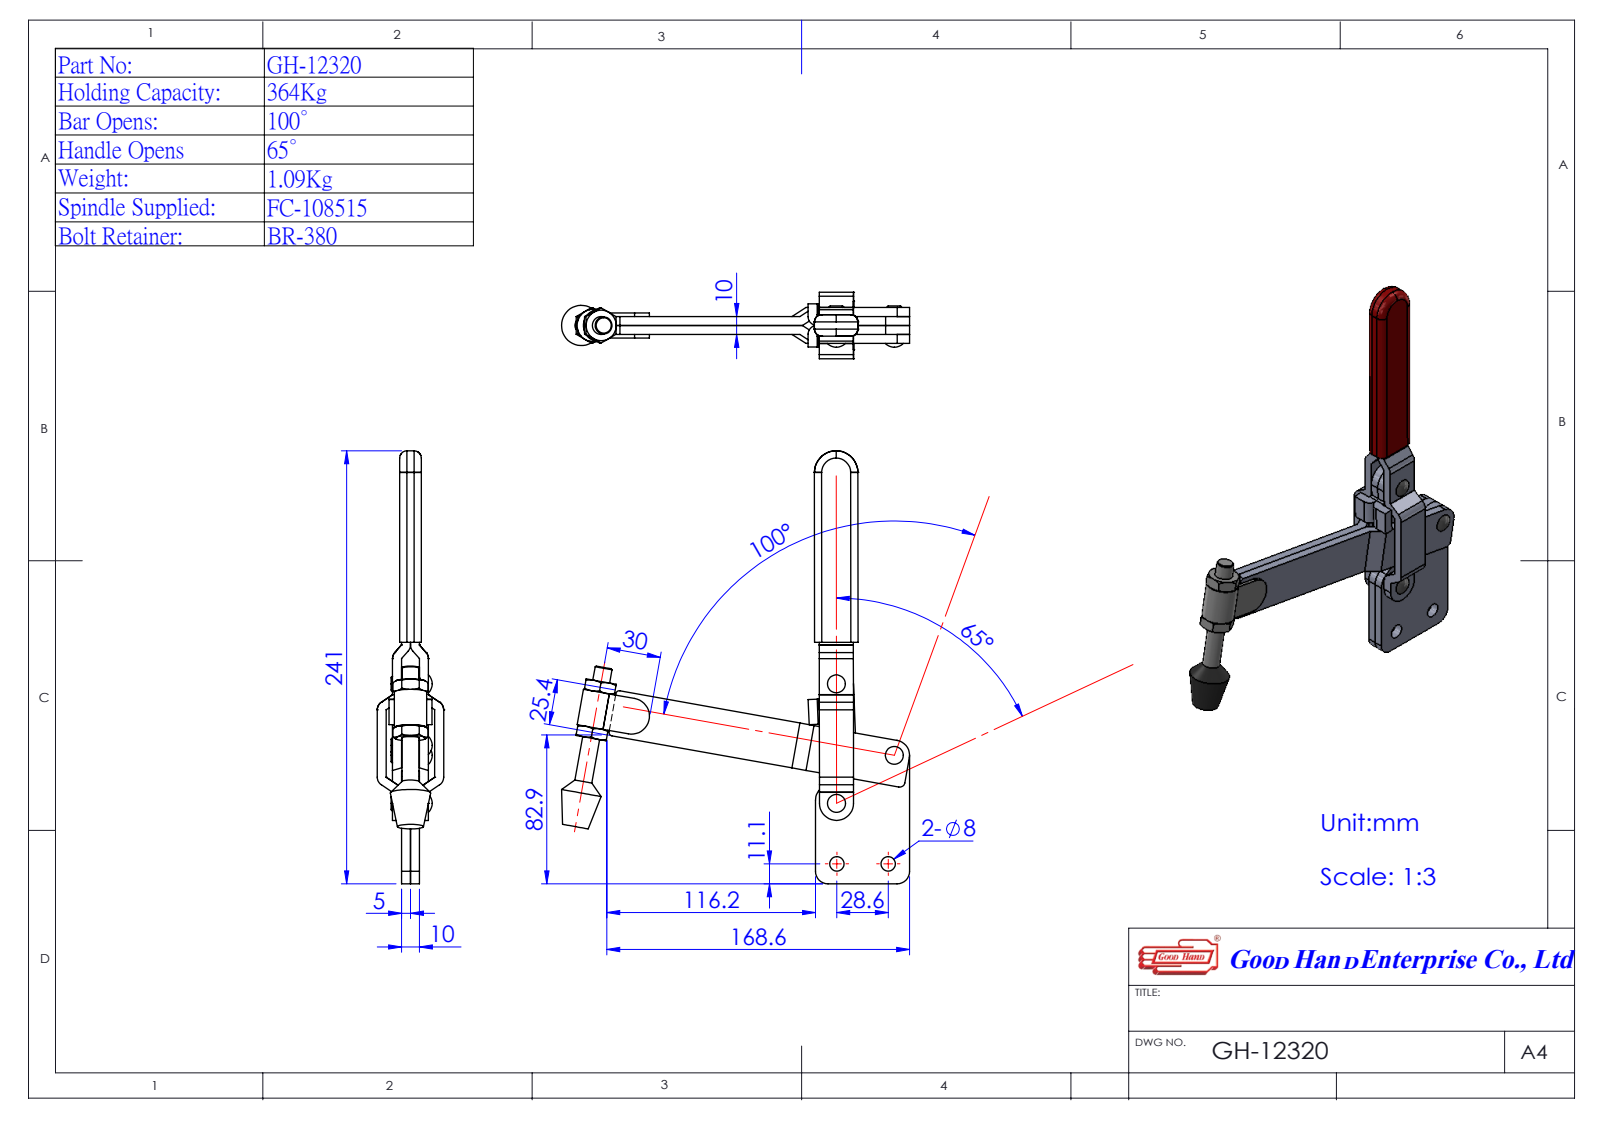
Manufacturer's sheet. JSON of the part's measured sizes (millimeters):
{"part_name": "GH-12320(簡化)-1; Group4^GH-12320(簡化)-1; Group1^GH-12320(簡化)-1; Group3^GH-12320(簡化)-1 (+2 more)", "step_written_by": "SolidWorks 2016 (AUTOMOTIVE_DESIGN)", "units": "millimeters", "bodies": {"solids": 5, "faces": 292, "planar": 129, "cylindrical": 115, "other": 48}, "overall_size": [240.39, 202.66, 37], "volume_mm3": 152696, "surface_area_mm2": 61042, "round_holes": [[4, 4], [8, 2], [6.3, 1]], "round_bosses_or_shafts": [[9.53, 1], [6.3, 1]], "partial_cylinders_radius": [[0.1, 10], [4, 8], [1, 4], [2, 4], [5.1, 4], [5.1, 4], [7, 3], [9.5, 3]], "face_to_face_distances": [5, 10, 1, 15, 6, 4, 8.5, 13.5, 18.5, 23.5], "hole_center_spacings": [28.6, 31.4, 32.25, 33.69, 34.31, 41.83, 44.32, 51.24]}
